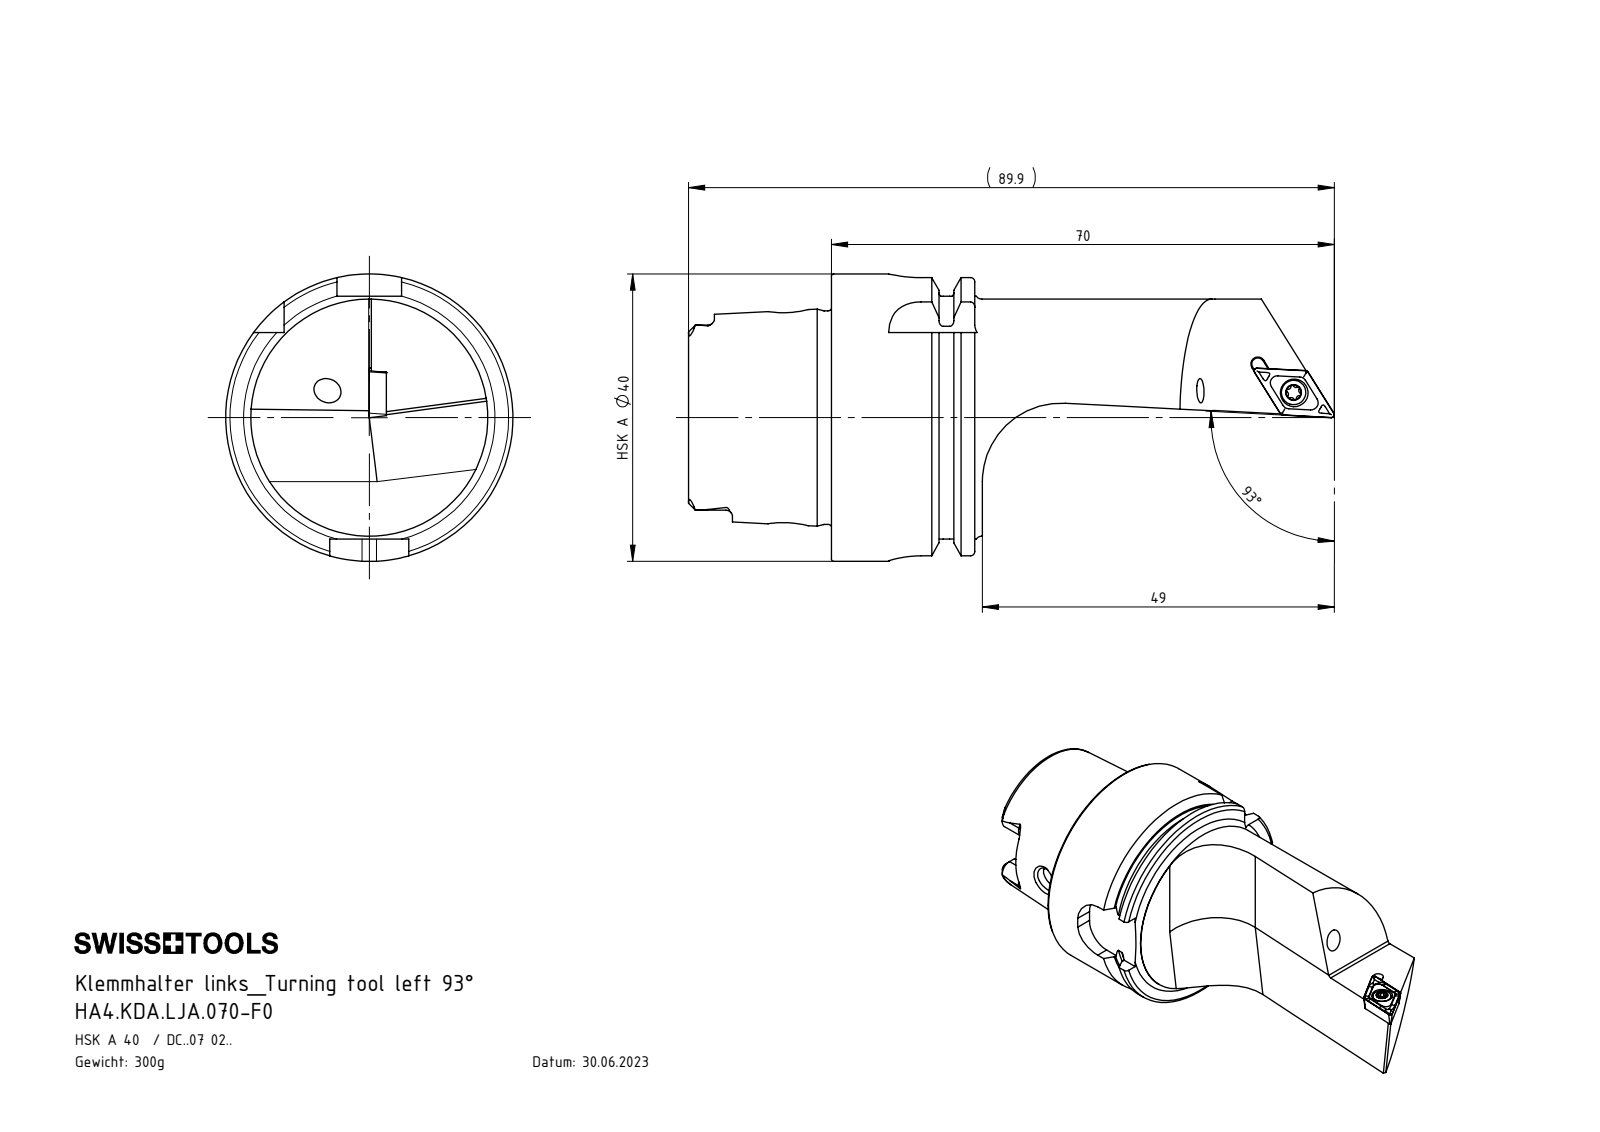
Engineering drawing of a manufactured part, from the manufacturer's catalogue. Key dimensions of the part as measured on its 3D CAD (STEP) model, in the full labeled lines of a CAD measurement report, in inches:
Part name (STEP PRODUCT): WCA-ER2.001.006_B; HA4-KDA.LJA.070-F0_A_Fertigbearbeitung; HA4.KDA.LJA.070-F0; KVT_MB_600_040 (+1 more)
STEP written by: SolidWorks 2017 (AUTOMOTIVE_DESIGN)
Units: inches
Bodies: 7 solids, 346 faces (83 planar, 100 cylindrical, 163 other)
Overall size (bounding box): 3.539 × 1.575 × 1.575
Volume: 2.339 in³ · Surface area: 21.58 in²
Round holes (diameter × count): ⌀0.13 ×3, ⌀0.118 ×2, ⌀0.157 ×2, ⌀0.081 ×1, ⌀0.11 ×1, ⌀0.152 ×1, ⌀0.181 ×1, ⌀0.394 ×1, ⌀0.433 ×1, ⌀0.492 ×1, ⌀0.827 ×1, ⌀1.004 ×1
Round bosses / shafts (diameter × count): ⌀0.157 ×2, ⌀1.575 ×1, ⌀1.368 ×1, ⌀1.299 ×1, ⌀1.17 ×1, ⌀0.134 ×1, ⌀0.098 ×1
Partial cylindrical surfaces — rounded edges, fillets, slot ends (radius × count): R0.008 ×6, R0.035 ×6, R0.014 ×5, R0.074 ×4, R0.177 ×4, R0.014 ×1, R0.02 ×1, R0.033 ×1
Main face-to-face distances: 0.313, 0.785, 0.472, 0.827, 0.514, 0.041, 0.783, 1.096, 1.569, 1.61
Hole centre spacings: 2.261, 2.265
